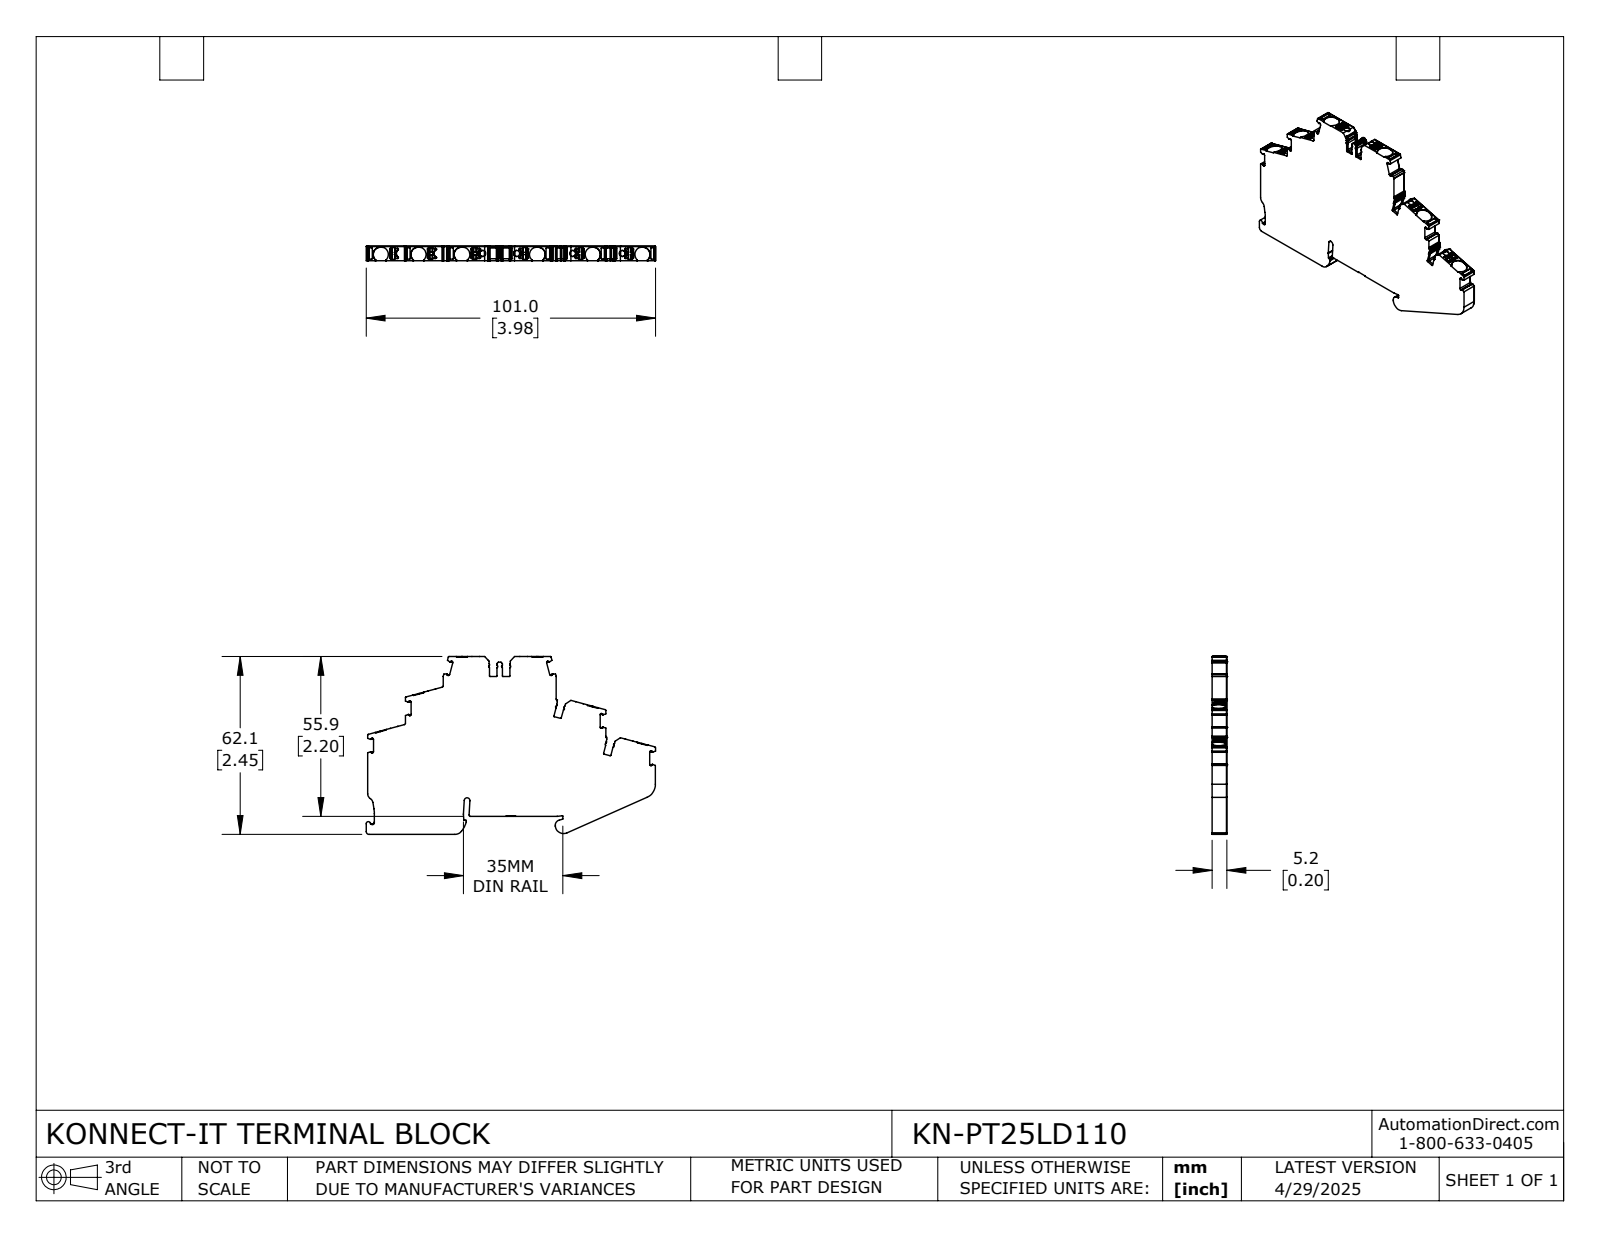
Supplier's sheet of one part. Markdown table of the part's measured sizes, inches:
| quantity | value |
| --- | --- |
| part name | KN-PT25LD110 |
| STEP written by | SolidWorks 2024 (CONFIG_CONTROL_DESIGN) |
| units | inches |
| bodies | 1 solid, 1212 faces (579 planar, 528 cylindrical, 105 other) |
| overall size | 3.977 × 2.445 × 0.203 |
| volume | 1.354 in³ |
| surface area | 16.76 in² |
| round holes (diameter × count) | 0.083 × 4 |
| partial cylindrical surfaces (radius × count) | 0.008 × 128, 0.004 × 49, 0.012 × 47, 0.02 × 26, 0.006 × 24, 0.016 × 17, 0.024 × 14, 0.006 × 12 |
| main face-to-face distances | 0.203, 0.246, 0.079, 2.191, 2.437, 0.319, 0.682, 0.519, 2.445, 2.199 |
| hole center spacings | 0.466, 0.792 |
